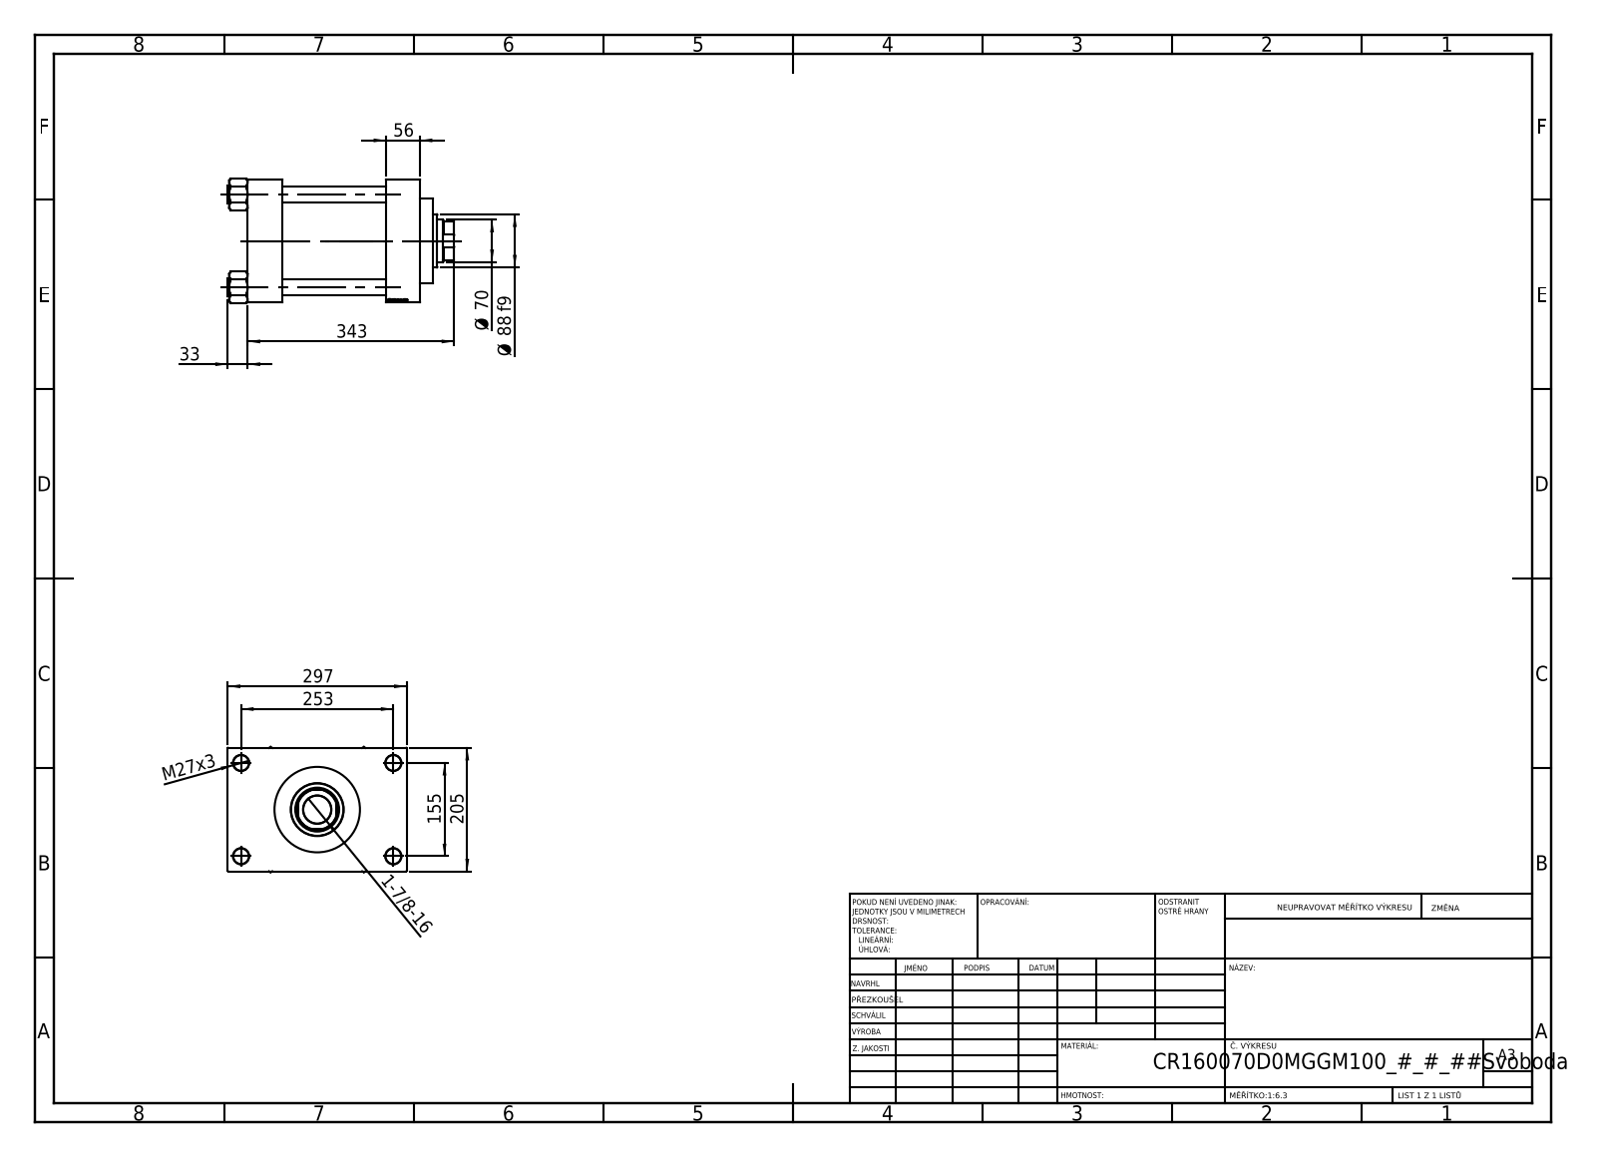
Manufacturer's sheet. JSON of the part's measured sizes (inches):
{"part_name": "V215CR_D_TYCINKA; NUT_M5_D; V215CR_VCP_D; V215_VC_A (+1 more)", "step_written_by": "SolidWorks 2019 (CONFIG_CONTROL_DESIGN)", "units": "inches", "bodies": {"solids": 11, "faces": 1149, "planar": 544, "cylindrical": 87, "other": 518}, "overall_size": [14.803, 11.693, 8.194], "volume_in3": 519.3, "surface_area_in2": 1320, "round_holes": [[1.024, 4], [1.063, 4], [0.276, 2], [1.309, 2], [1.772, 2], [1.831, 1], [2.756, 1], [2.874, 1], [4.724, 1], [5.591, 1], [6.299, 1]], "round_bosses_or_shafts": [[1.181, 4], [6.535, 1], [3.465, 1]], "partial_cylinders_radius": [[1.339, 1]], "face_to_face_distances": [2.283, 9.055, 6.772, 11.26, 8.976, 2.205, 8.071, 1.811, 9.882, 2.835], "hole_center_spacings": [1.931, 4.312, 5.841, 6.098, 6.399, 8.03, 10.084, 6.102]}
